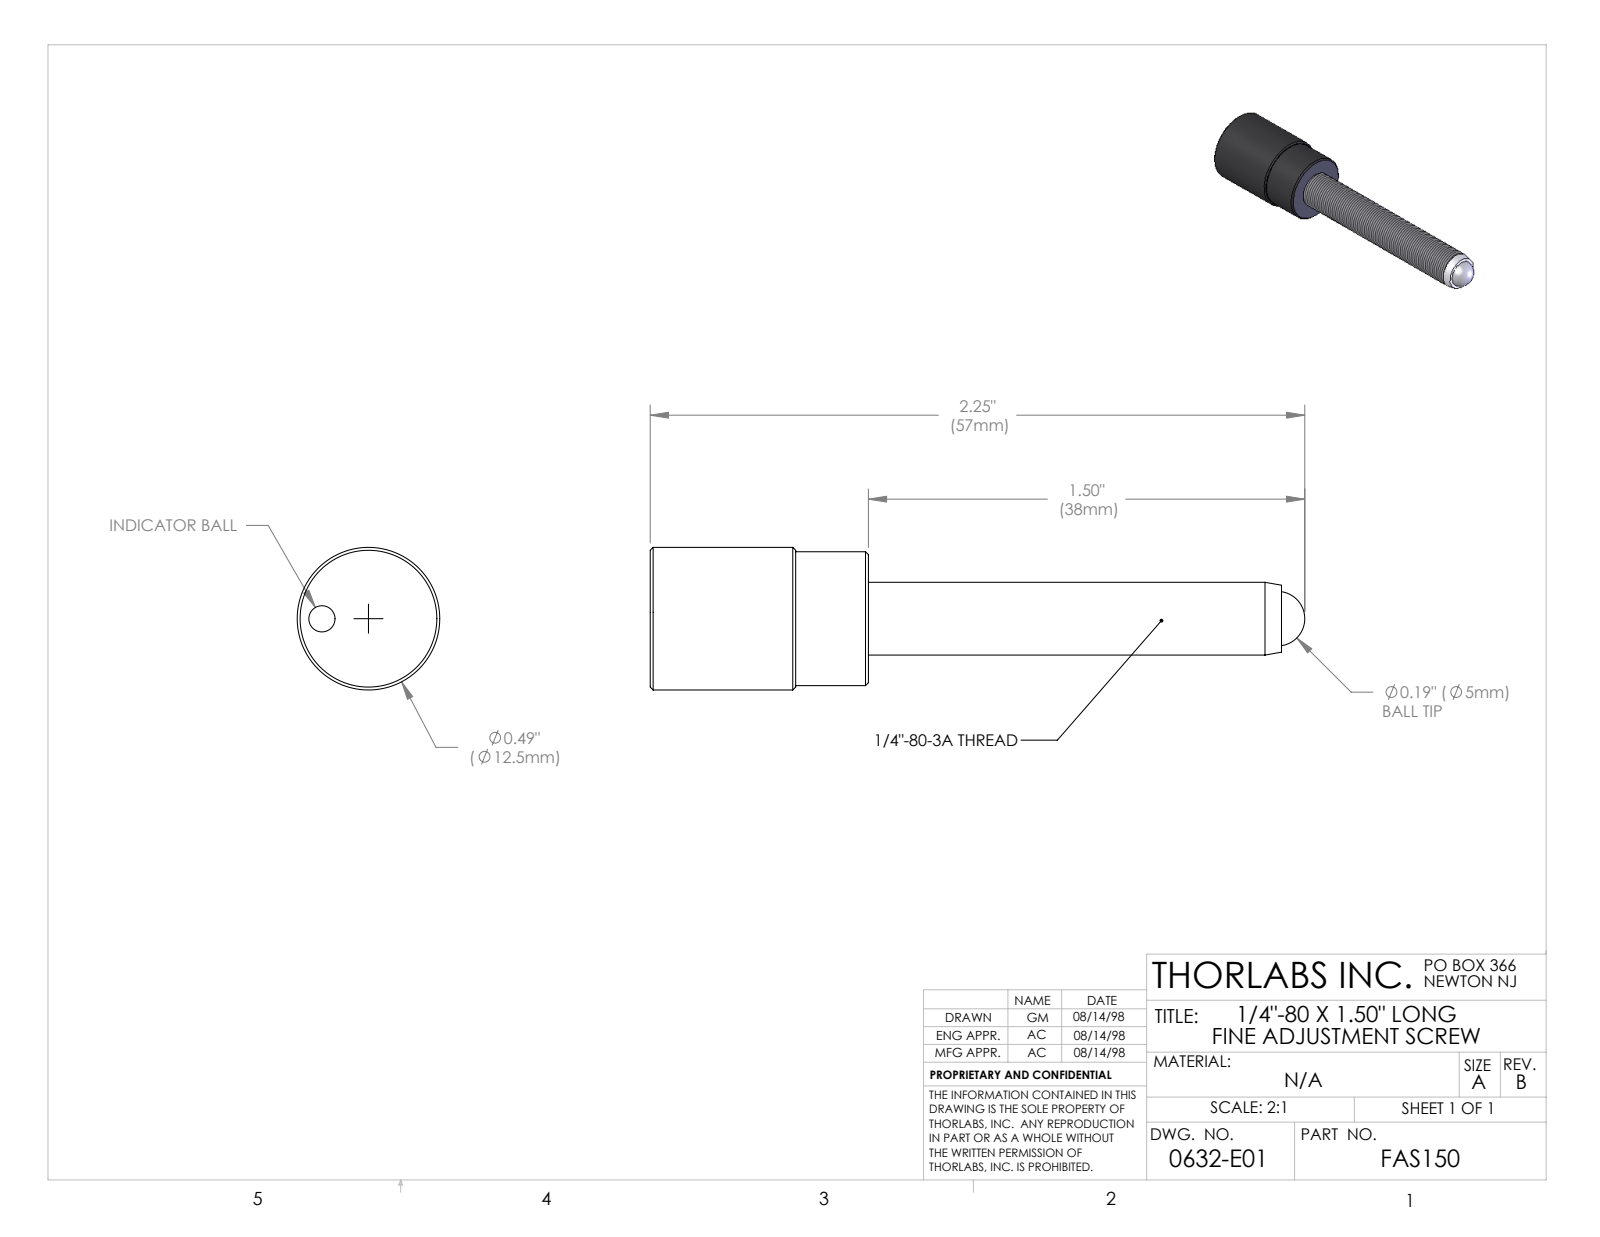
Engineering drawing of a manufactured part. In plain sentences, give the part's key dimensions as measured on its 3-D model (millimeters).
The part is named "0632-E0W". Its 3-D file was written by "SolidWorks 2007 (AUTOMOTIVE_DESIGN)". It is 4 solids with 40 faces: 8 planar, 14 cylindrical and 18 other. Overall it measures 57.15 by 12.45 by 12.45 millimeters. Its volume is 3 406 cubic millimeters and its surface area 2 360 square millimeters. Round holes: 1 of diameter 2.29, 1 of diameter 4.78, 1 of diameter 5.94, 1 of diameter 6.3. Round bosses or shafts: 1 of diameter 12.45, 1 of diameter 11.68, 1 of diameter 6.35. The main face-to-face distances are 19.05, 6.35, 12.7, 55.12, 48.77, 36.07, 42.42, 2.29, 4.06, 10.41. The hole center spacings are 4.07.
